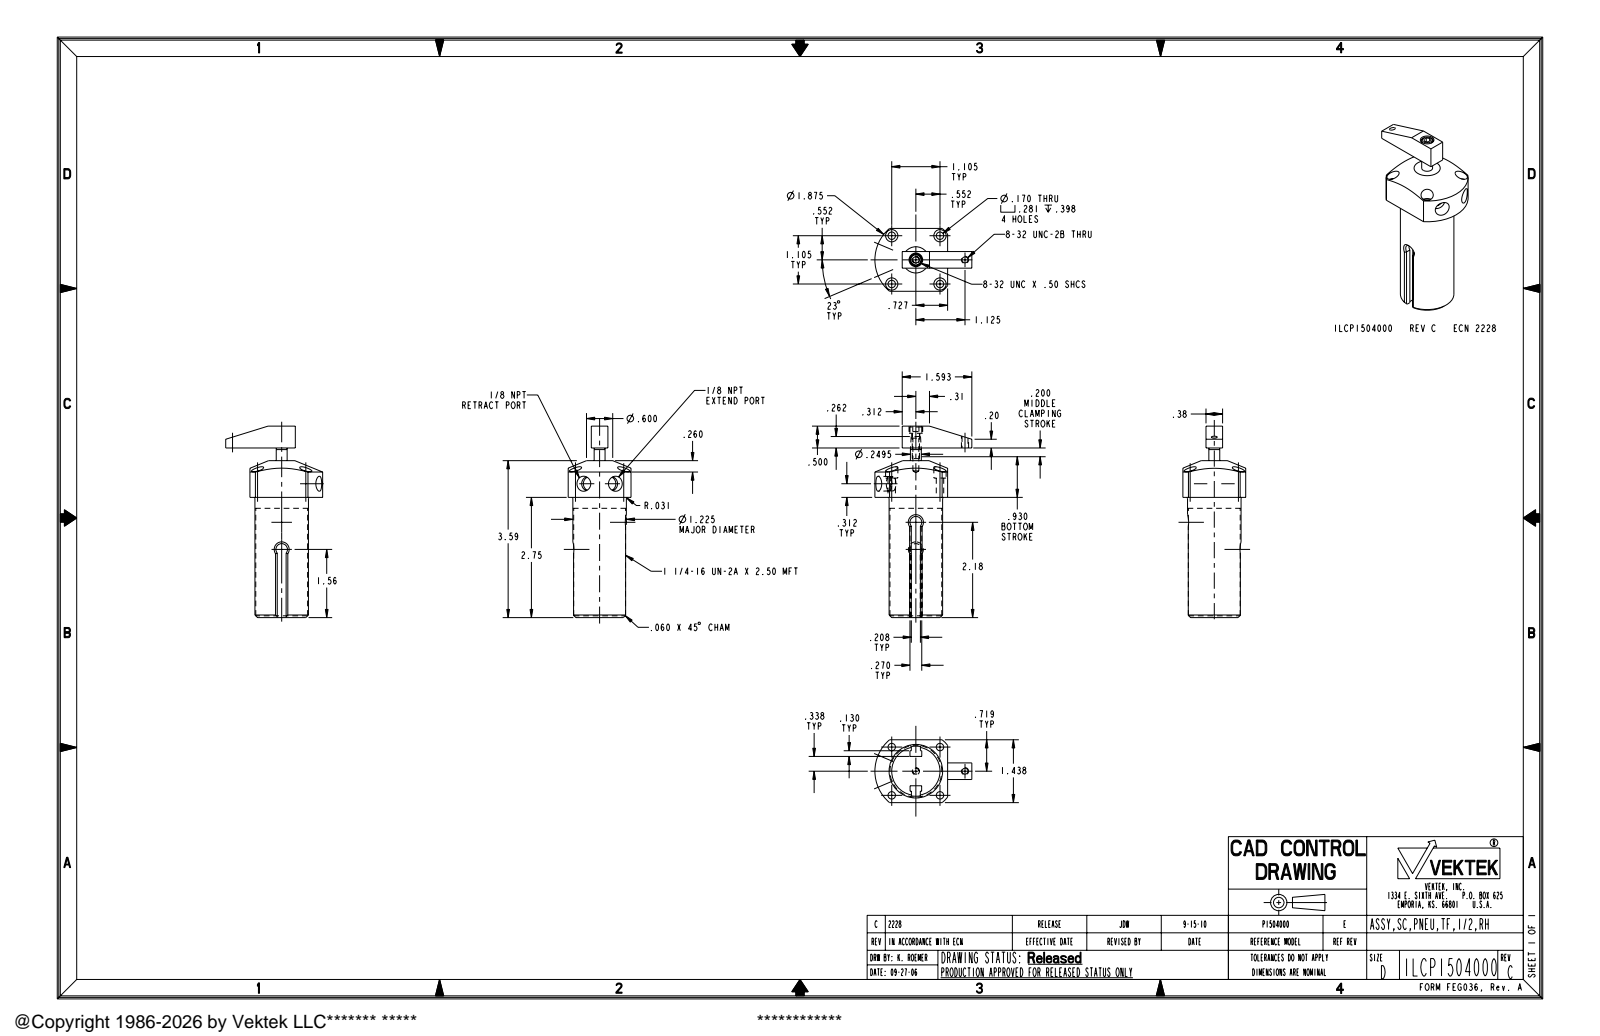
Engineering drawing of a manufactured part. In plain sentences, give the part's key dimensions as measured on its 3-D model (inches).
The part is named "ILCP1504000; ILC91500503; ILCP1504000_ASM". Its 3-D file was written by "PRO/ENGINEER BY PARAMETRIC TECHNOLOGY CORPORATION, 2007460 (AUTOMOTIVE_DESIGN_CC2)". It is 2 solids with 123 faces: 52 planar, 47 cylindrical and 24 other. Overall it measures 4.38 by 2.219 by 1.438 inches. Its volume is 4.675 cubic inches and its surface area 36.84 square inches. Round holes: 4 of diameter 0.17, 4 of diameter 0.281, 2 of diameter 0.136, 2 of diameter 0.328, 1 of diameter 0.18, 1 of diameter 0.312. Round bosses or shafts: 2 of diameter 0.164, 1 of diameter 1.225, 1 of diameter 1.187, 1 of diameter 0.27, 1 of diameter 0.25. Partial cylindrical surfaces (rounded edges, fillets, slot ends): 1 of radius 0.132, 1 of radius 0.135, 1 of radius 0.937. The main face-to-face distances are 0.529, 0.909, 2.75, 1.438, 0.031, 0.237, 0.38, 1.057, 0.528, 0.148. The hole center spacings are 0.781, 1.105, 0.796, 1.562, 1.766, 1.125.
